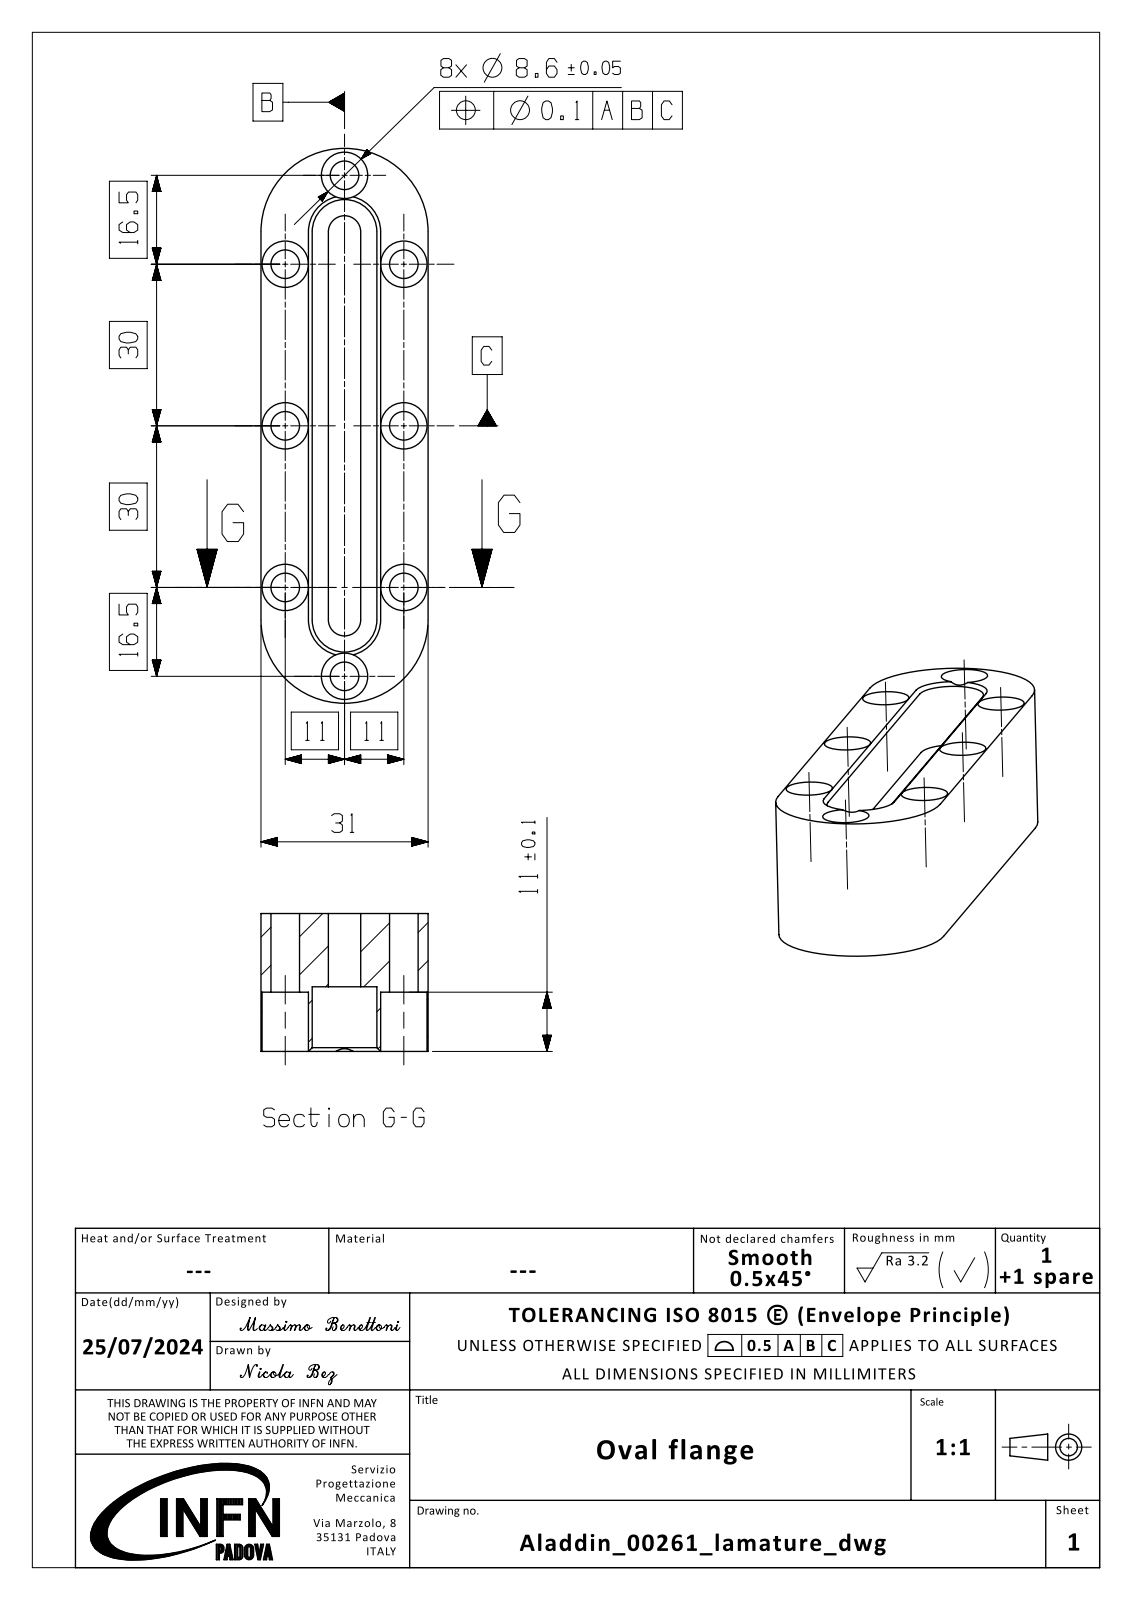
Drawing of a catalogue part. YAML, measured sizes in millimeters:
part_name: "IR3_00000261_v5_lamature_objects"
step_written_by: "SIEMENS PLM Software NX2306.9102 (AUTOMOTIVE_DESIGN)"
units: millimeters
bodies: {solids: 1, faces: 43, planar: 19, cylindrical: 22, other: 2}
overall_size: [103, 31, 25.6]
volume: 50743
surface_area: 19520
round_holes:
  - {diameter: 5.3, count: 8}
  - {diameter: 8.6, count: 8}
partial_cylinders:
  - {radius: 3, count: 2}
  - {radius: 6, count: 2}
  - {radius: 15.5, count: 2}
face_to_face_distances: [12.5, 18.5, 31, 9.5, 21.5, 3, 9, 25.6, 12, 6]
hole_center_spacings: [19.83, 30, 37.2, 47.78, 77.29, 22, 60, 63.91]
